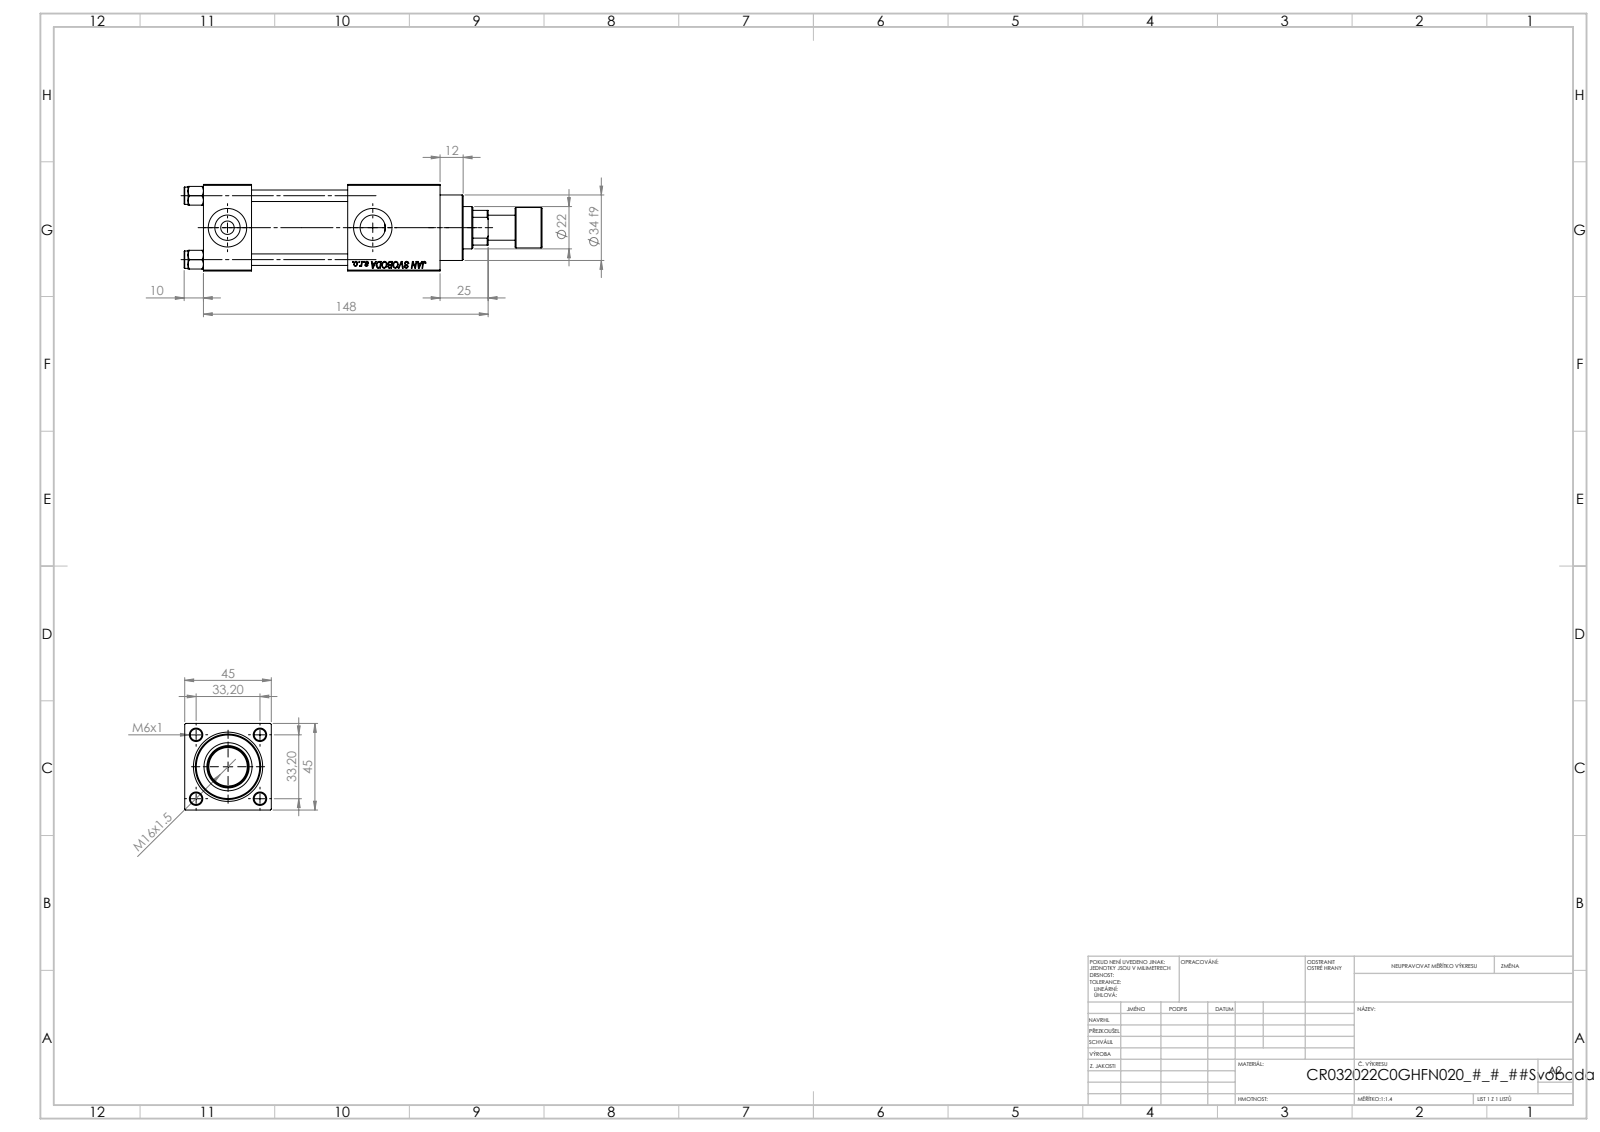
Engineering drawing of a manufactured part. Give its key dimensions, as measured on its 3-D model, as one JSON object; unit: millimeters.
{"part_name": "NUT_M5_C; V215CR_VCP_C; V215CR_C_TYCINKA; V215CR_C_Body (+2 more)", "step_written_by": "SolidWorks 2019 (CONFIG_CONTROL_DESIGN)", "units": "millimeters", "bodies": {"solids": 12, "faces": 1158, "planar": 528, "cylindrical": 90, "other": 540}, "overall_size": [186, 45, 45], "volume_mm3": 216560, "surface_area_mm2": 73462, "round_holes": [[6, 4], [7, 2], [13.16, 2], [20, 2], [10.5, 1], [22, 1], [24, 1], [25, 1], [32, 1], [33, 1]], "round_bosses_or_shafts": [[9, 4], [38, 1], [34, 1], [21, 1], [13, 1]], "face_to_face_distances": [45, 25, 123, 50, 75, 98, 48, 94.3, 69.3, 19.3], "hole_center_spacings": [23.48, 33.2, 46.95, 75.5]}
